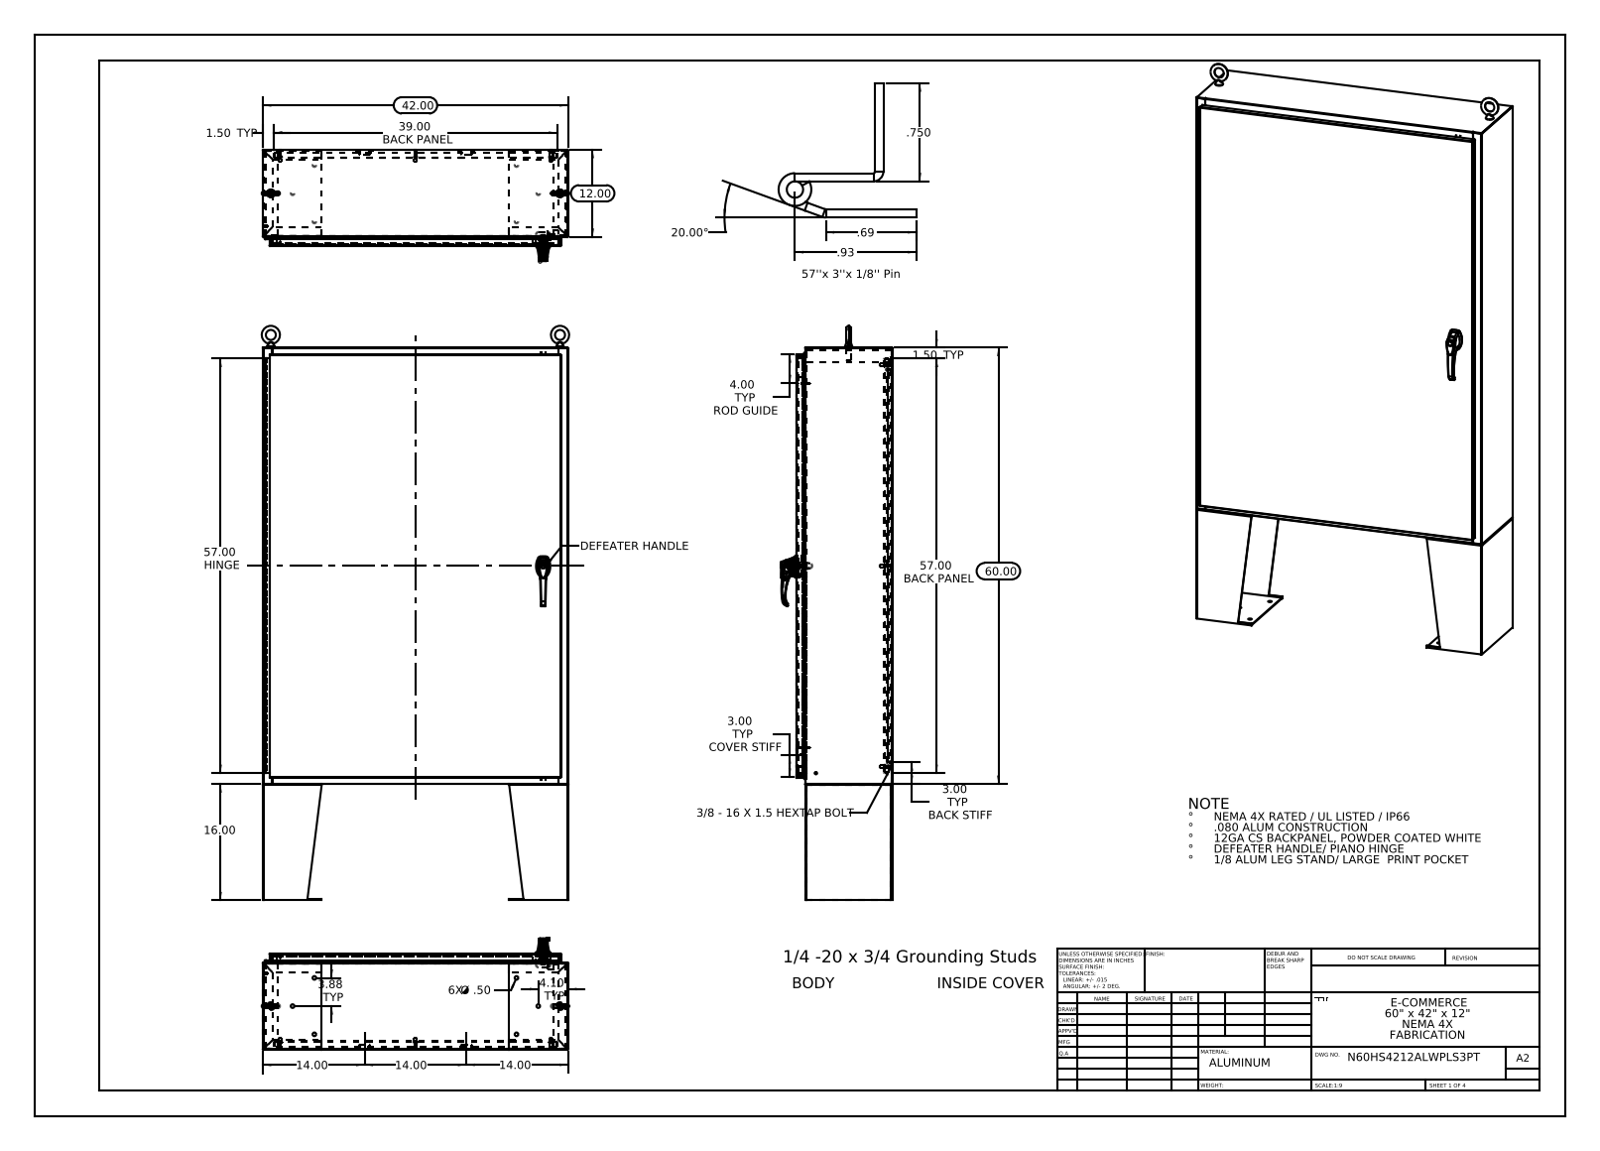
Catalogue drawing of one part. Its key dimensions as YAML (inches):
part_name: "Eye-Bolt_Stiffener WMT Template 1913; N60HS4212SSWPLS3PT SD-LSK-ASSY; 012103_012102; N60HS4212SSWPLS3PT (+8 more)"
step_written_by: "SolidWorks 2013 (CONFIG_CONTROL_DESIGN)"
units: inches
bodies: {solids: 55, faces: 3808, planar: 1529, cylindrical: 1461, other: 818}
overall_size: [79, 42.271, 15.307]
volume: 1029
surface_area: 24725
round_holes:
  - {diameter: 0.5, count: 14}
  - {diameter: 0.25, count: 10}
  - {diameter: 0.75, count: 4}
  - {diameter: 0.138, count: 3}
  - {diameter: 0.161, count: 3}
  - {diameter: 0.079, count: 2}
  - {diameter: 0.203, count: 2}
  - {diameter: 0.313, count: 2}
  - {diameter: 0.437, count: 2}
  - {diameter: 0.125, count: 1}
  - {diameter: 0.125, count: 1}
  - {diameter: 0.197, count: 1}
round_bosses_or_shafts:
  - {diameter: 0.625, count: 10}
  - {diameter: 0.157, count: 10}
  - {diameter: 0.14, count: 10}
  - {diameter: 0.375, count: 8}
  - {diameter: 0.33, count: 8}
  - {diameter: 0.315, count: 3}
  - {diameter: 0.236, count: 3}
  - {diameter: 1.181, count: 1}
partial_cylinders:
  - {radius: 0.118, count: 37}
  - {radius: 0.013, count: 34}
  - {radius: 0.006, count: 33}
  - {radius: 0.088, count: 28}
  - {radius: 0.039, count: 15}
  - {radius: 0.028, count: 12}
  - {radius: 0.039, count: 8}
  - {radius: 0.143, count: 8}
face_to_face_distances: [0.075, 13.126, 0.104, 13.051, 1.075, 13.201, 1, 12.126, 12.051, 1.179]
hole_center_spacings: [7.137, 16.578, 23.354, 25.662, 27.625, 31.035, 33.317, 34.004]
